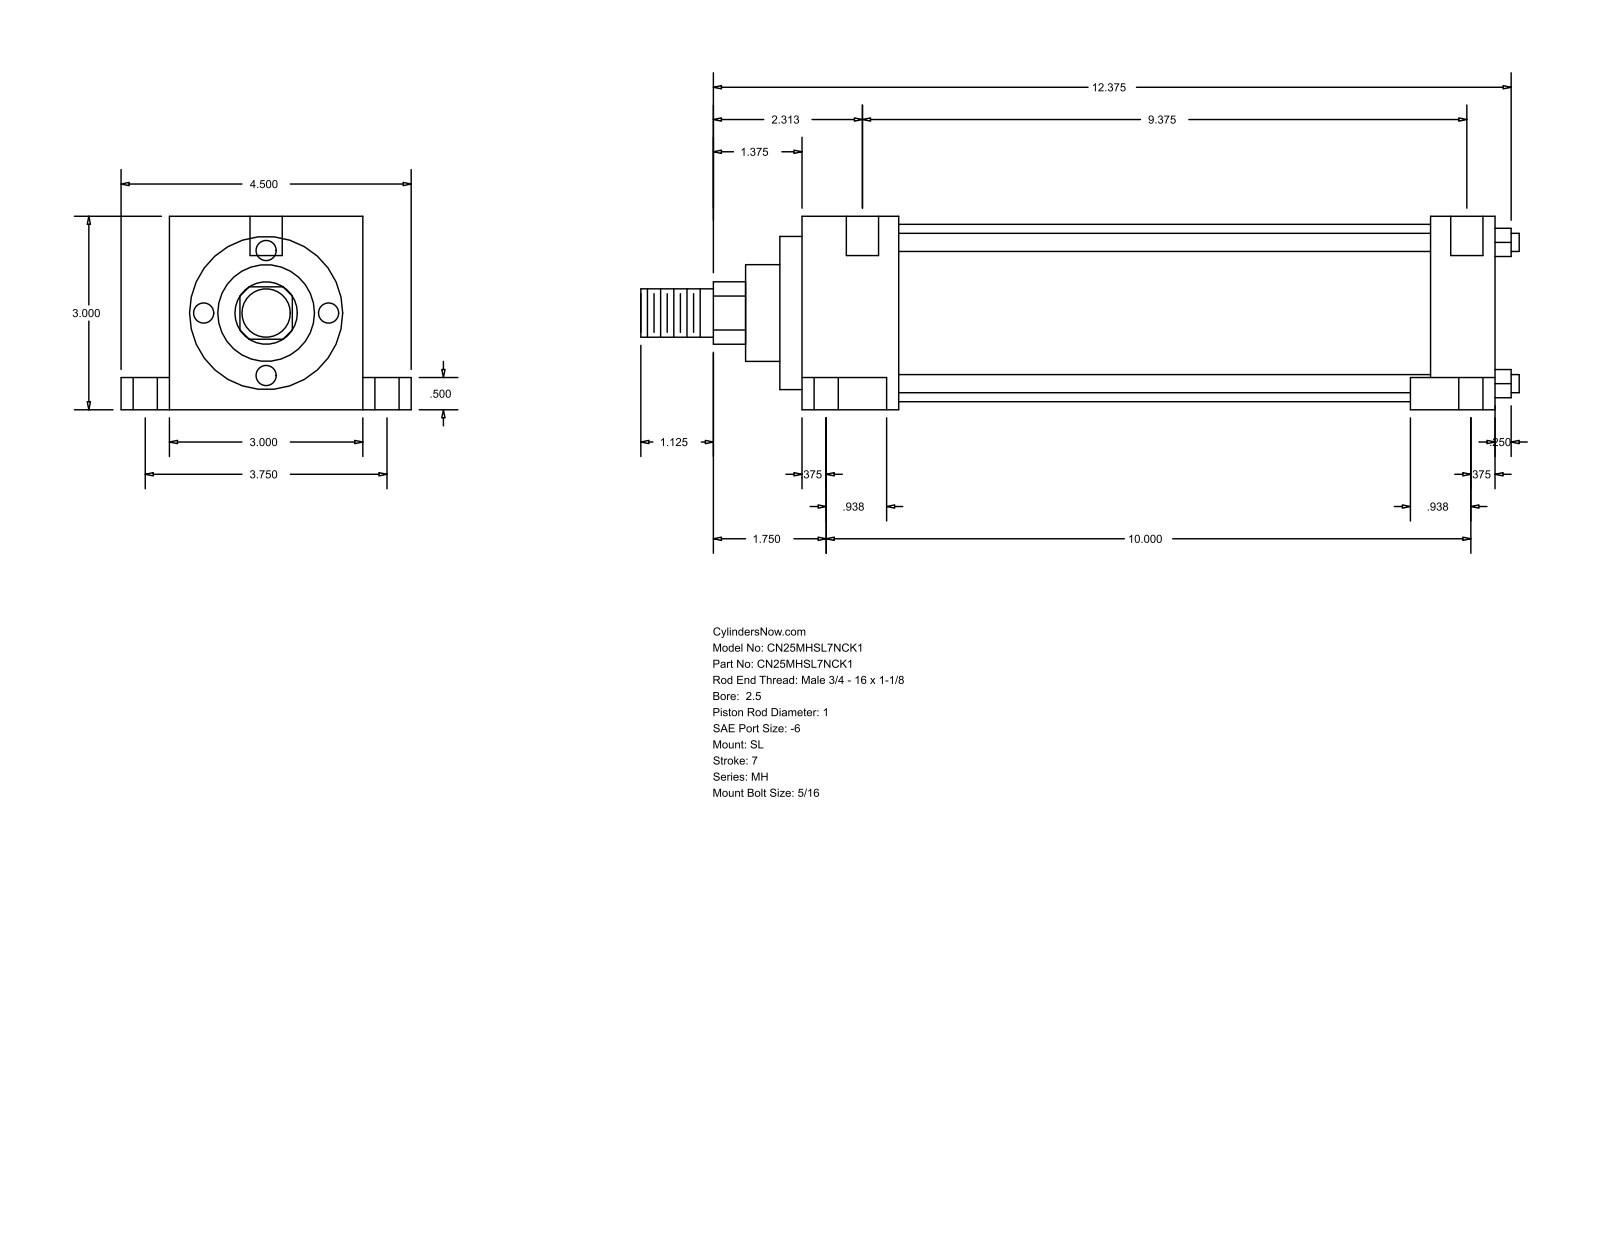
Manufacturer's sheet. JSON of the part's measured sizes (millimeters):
{"part_name": "MH_SL__0250_1", "step_written_by": "GSSL Pune (CONFIG_CONTROL_DESIGN)", "units": "millimeters", "bodies": {"solids": 0, "faces": 86, "planar": 61, "cylindrical": 25, "other": 0}, "overall_size": [346.07, 114.3, 76.2], "round_holes": [[5.56, 2], [9.53, 2], [15.88, 2], [12.7, 1]], "round_bosses_or_shafts": [[7.14, 4], [69.85, 1], [60.33, 1], [38.1, 1], [25.4, 1], [19.05, 1]], "partial_cylinders_radius": [[12.29, 1]], "face_to_face_distances": [76.2, 25.41, 256.38, 281.79, 12.7, 63.5, 19.05, 95.25, 13.49, 269.87], "hole_center_spacings": [47.65, 3.18, 95.24]}
